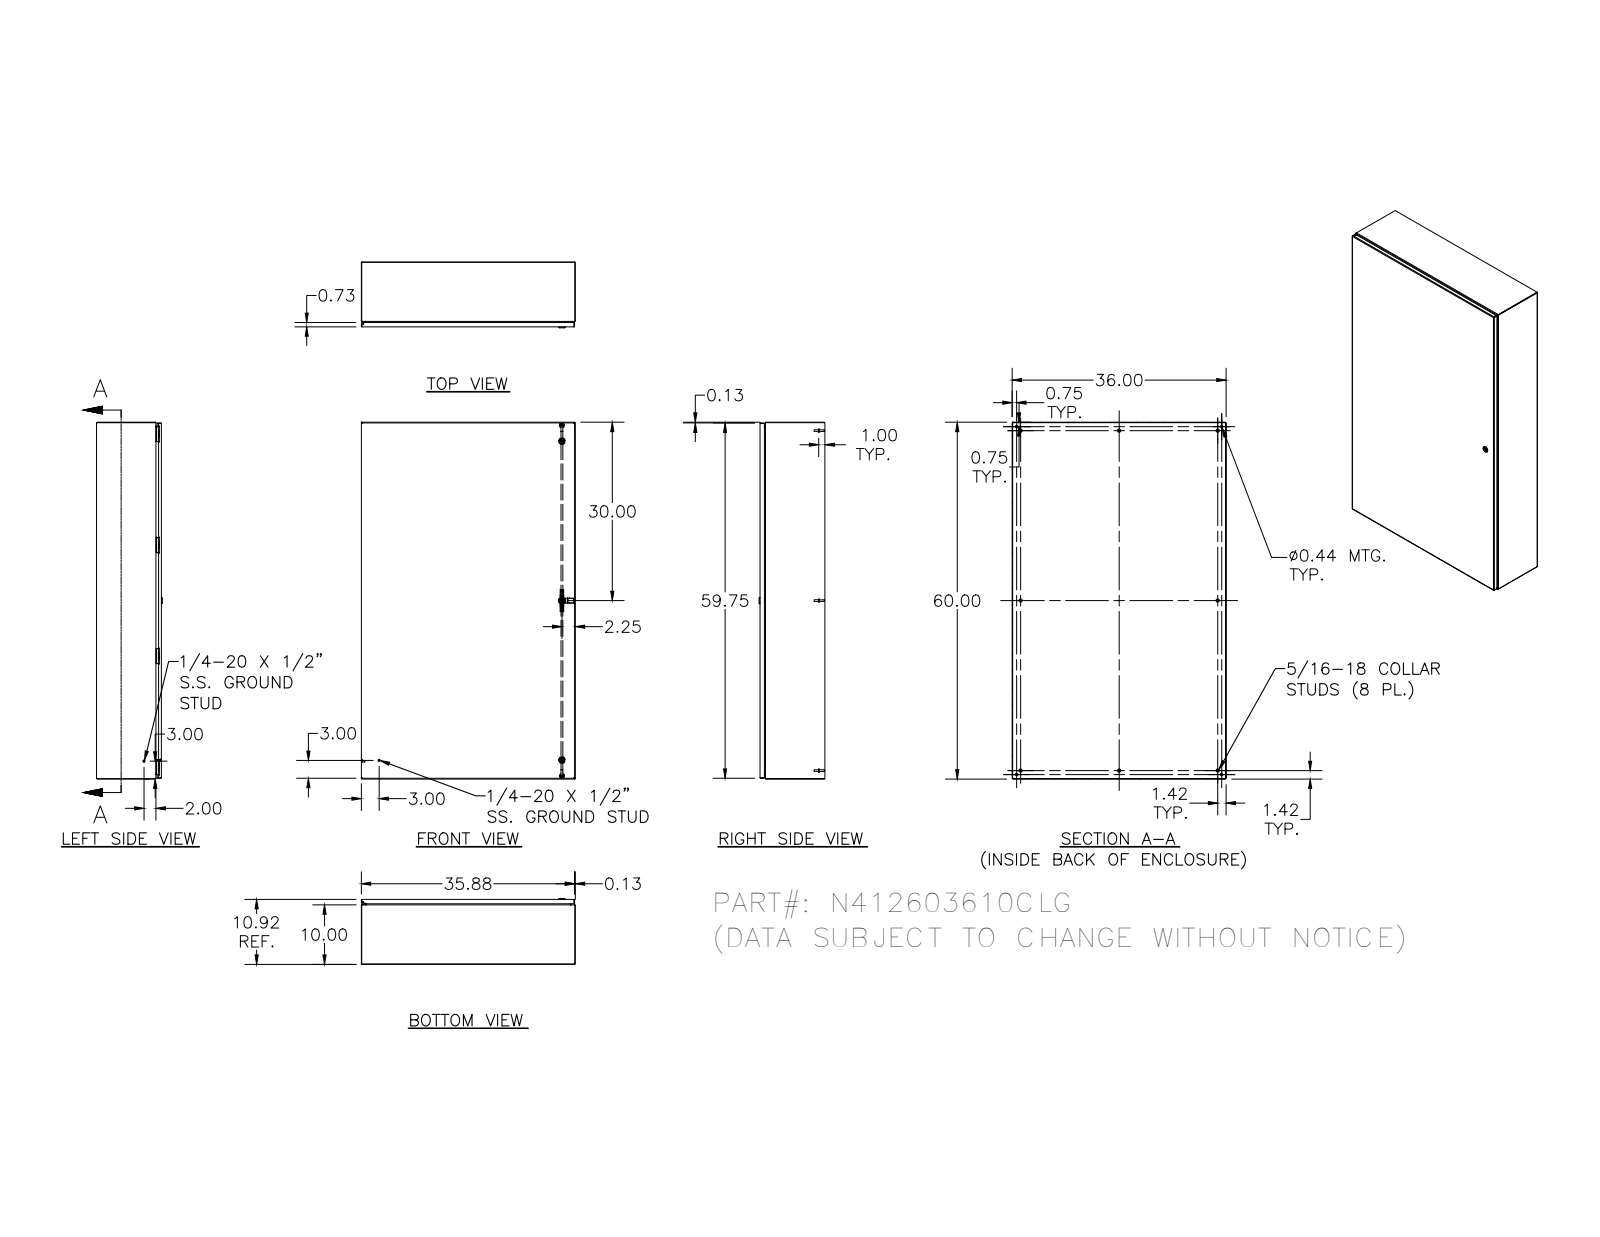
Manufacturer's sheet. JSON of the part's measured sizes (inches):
{"part_name": "N412603610C; N412603610CBLR; N4123610CTB; N4126036CLID (+8 more)", "step_written_by": "Autodesk Inventor 2011 (AUTOMOTIVE_DESIGN)", "units": "inches", "bodies": {"solids": 81, "faces": 2661, "planar": 988, "cylindrical": 992, "other": 681}, "overall_size": [60, 36, 11.075], "volume_in3": 496, "surface_area_in2": 13378, "round_holes": [[0.188, 9], [0.093, 8], [0.152, 8], [0.167, 8], [0.172, 8], [0.197, 5], [0.156, 4], [0.165, 4], [0.438, 4], [0.106, 2], [0.16, 2], [0.169, 2]], "round_bosses_or_shafts": [[0.25, 18], [0.563, 8], [0.36, 8], [0.32, 8], [0.3, 8], [0.275, 8], [0.256, 8], [0.164, 8]], "partial_cylinders_radius": [[0.05, 50], [0.031, 36], [0.016, 34], [0.125, 32], [0.012, 31], [0.02, 20], [0.105, 18], [0.032, 16]], "face_to_face_distances": [0.074, 10.843, 10.769, 10.917, 35.926, 59.926, 35.852, 36, 59.852, 60], "hole_center_spacings": [18.667, 37.333, 18.67, 18.667, 37.337, 0.5, 0.656, 0.66]}
